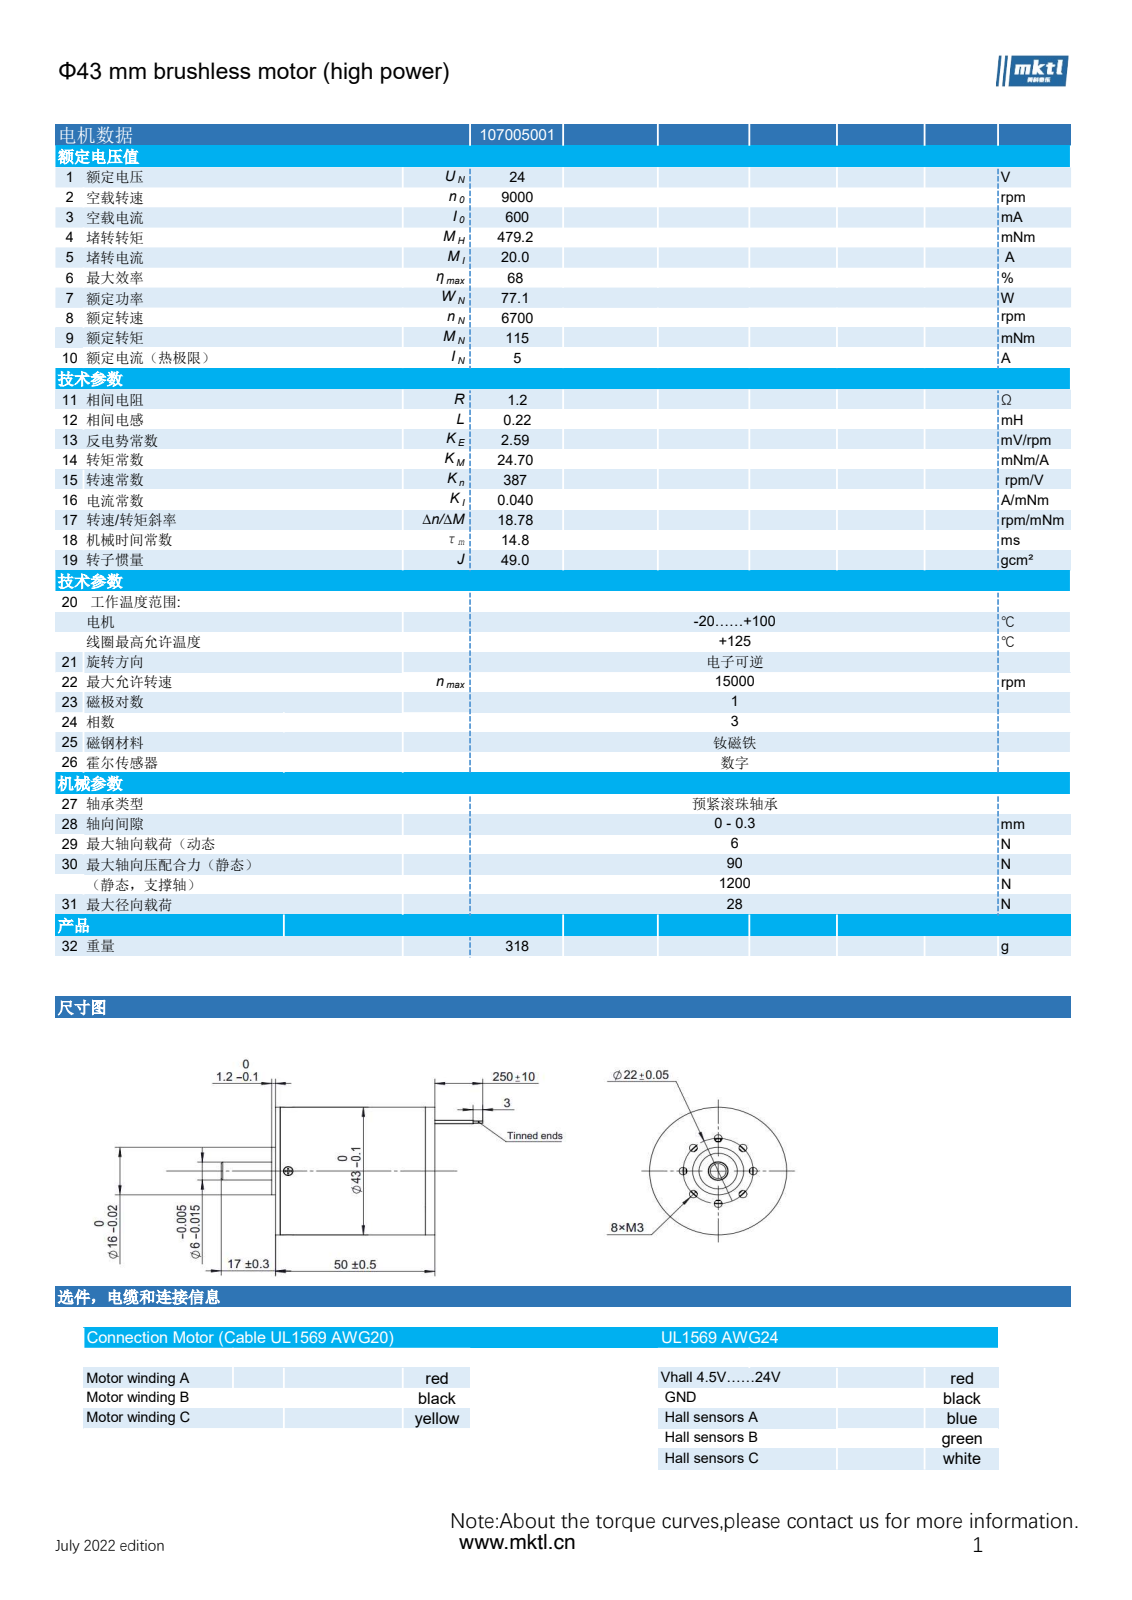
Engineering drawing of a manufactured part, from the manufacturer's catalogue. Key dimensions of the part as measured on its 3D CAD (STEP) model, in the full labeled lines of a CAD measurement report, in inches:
Part name (STEP PRODUCT): 107005001
STEP written by: SolidWorks 2025 (AUTOMOTIVE_DESIGN)
Units: inches
Bodies: 206 solids, 2264 faces (875 planar, 1265 cylindrical, 124 other)
Overall size (bounding box): 3.228 × 1.693 × 1.693
Volume: 3.899 in³ · Surface area: 369.9 in²
Round holes (diameter × count): ⌀0.039 ×9, ⌀0.059 ×8, ⌀0.098 ×8, ⌀0.033 ×5, ⌀0.047 ×5, ⌀0.083 ×3, ⌀0.087 ×3, ⌀0.118 ×3, ⌀0.122 ×2, ⌀0.236 ×1, ⌀0.413 ×1, ⌀0.472 ×1
Round bosses / shafts (diameter × count): ⌀0.024 ×5, ⌀0.157 ×3, ⌀0.063 ×3, ⌀0.031 ×3, ⌀0.02 ×3, ⌀0.11 ×2, ⌀0.055 ×2, ⌀0.051 ×2
Partial cylindrical surfaces — rounded edges, fillets, slot ends (radius × count): R0.004 ×24, R0.039 ×21, R0.012 ×3, R0.02 ×2, R0.079 ×1, R0.24 ×1, R0.26 ×1, R0.281 ×1
Main face-to-face distances: 0.016, 0.024, 0.031, 0.039, 0.047, 0.055, 0.063, 0.071, 0.079, 0.087
Hole centre spacings: 0.331, 0.433, 0.613, 0.8, 0.079, 1.039, 0.236, 0.63
